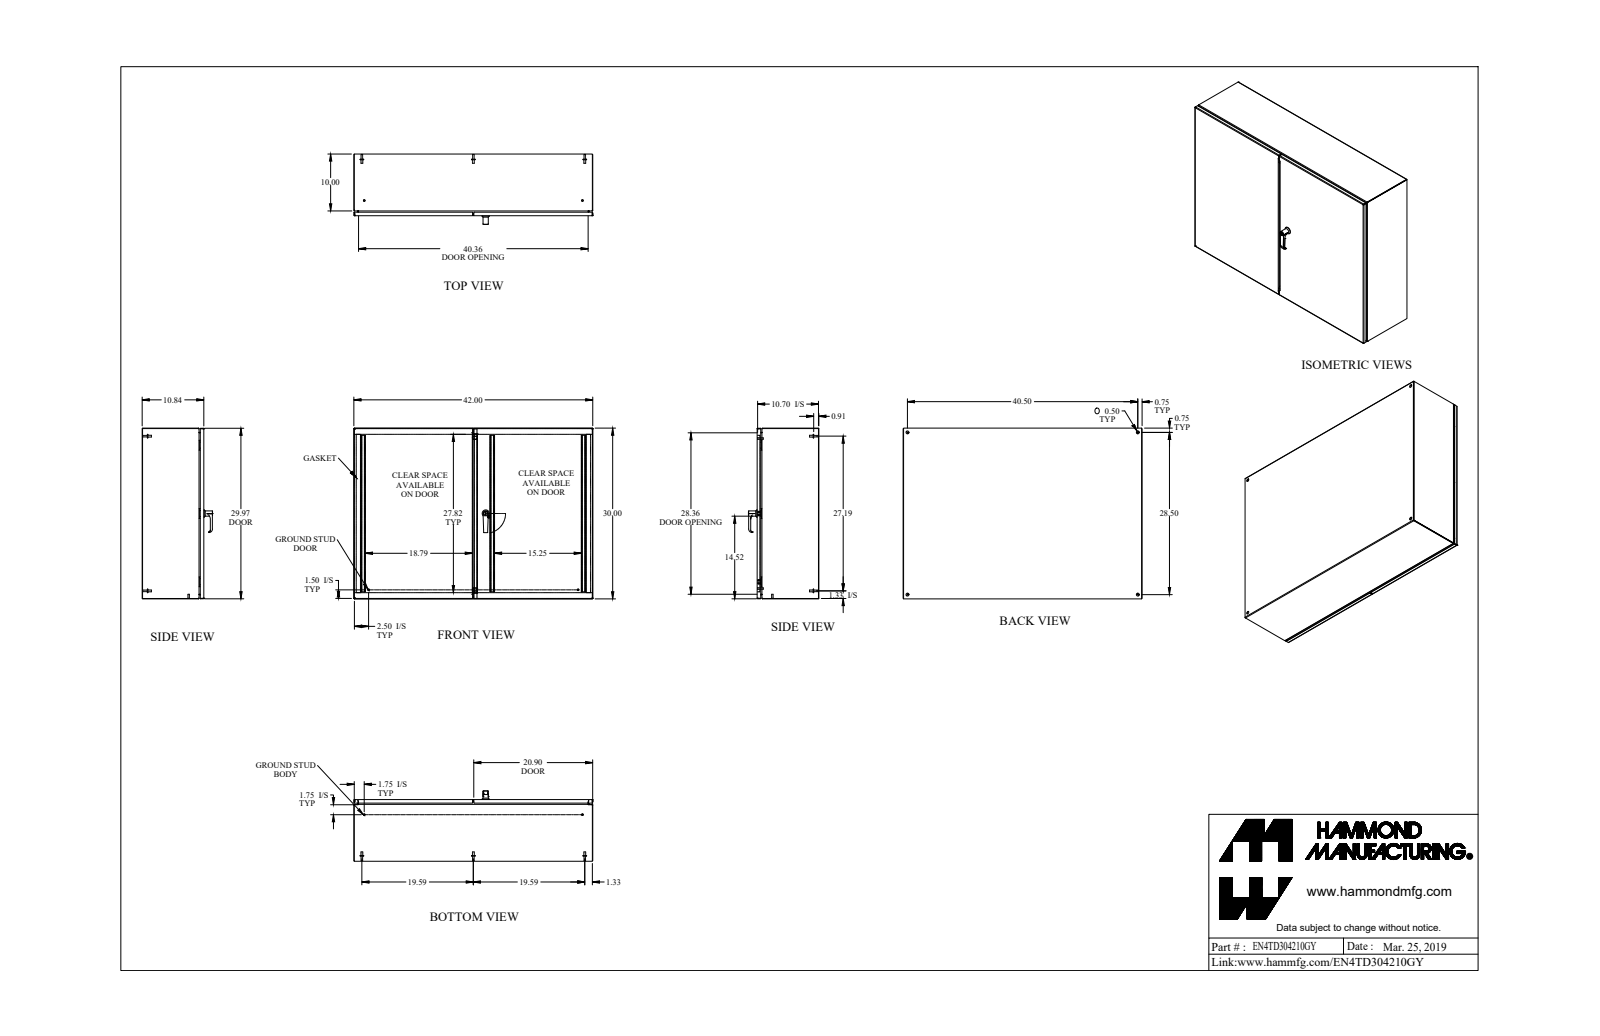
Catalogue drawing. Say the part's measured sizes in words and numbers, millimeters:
The part is named "EN4TD304210GY". Its 3-D file was written by "SolidWorks 2018 (AUTOMOTIVE_DESIGN)". It is 85 solids with 2139 faces: 955 planar, 790 cylindrical and 394 other. Overall it measures 1066.8 by 762 by 314.2 millimeters. Its volume is 5 894 000 cubic millimeters and its surface area 6 086 000 square millimeters. Round holes: 5 of diameter 5, 4 of diameter 4.5, 4 of diameter 6.7, 4 of diameter 12.7, 3 of diameter 6.1, 3 of diameter 6.1, 2 of diameter 4.4, 2 of diameter 6.4, 2 of diameter 6.5, 2 of diameter 6.6, 2 of diameter 8, 2 of diameter 10. Round bosses or shafts: 12 of diameter 6.4, 8 of diameter 8, 6 of diameter 15.9, 6 of diameter 6.9, 4 of diameter 13, 4 of diameter 7.1, 4 of diameter 4, 3 of diameter 19.1. Partial cylindrical surfaces (rounded edges, fillets, slot ends): 30 of radius 1.6, 26 of radius 0.9, 26 of radius 2.7, 20 of radius 2.4, 18 of radius 0.4, 18 of radius 1.1, 18 of radius 2.1, 16 of radius 0.5. The main face-to-face distances are 1.8, 273.6, 271.7, 275.4, 760.2, 1065, 758.3, 762, 1063.1, 1066.8. The hole center spacings are 20, 335, 452.2, 578, 584.8, 674.7, 723.9, 1028.7.
